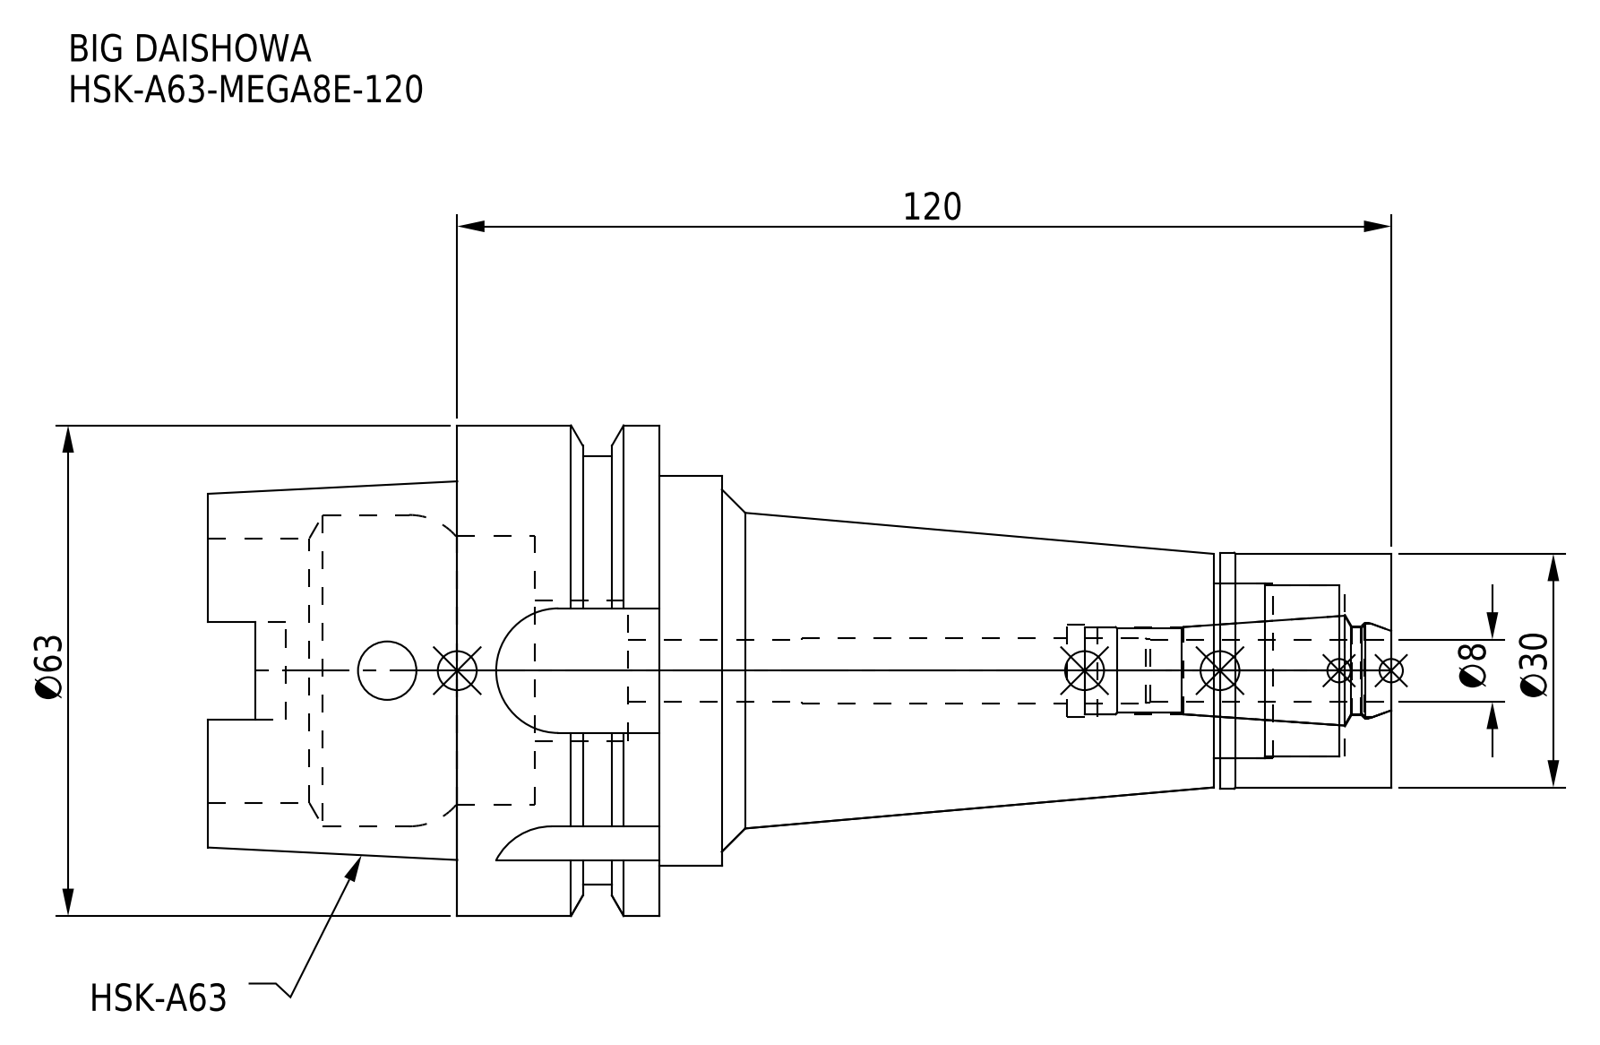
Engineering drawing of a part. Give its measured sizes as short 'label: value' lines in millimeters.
name: HA63ME08120-080_ASM.stp; HSK-A63-MEGA8E-120_1.stp; DXF_TEMP_ASSY_ASM_4_ASM.stp; HSK-A63-MEGA8E-120-080-FreeParts (+3 more)
written by: SolidWorks 2019 (CONFIG_CONTROL_DESIGN)
unit: mm
bodies: 2 solids, 127 faces (45 planar, 54 cylindrical, 28 other)
size: 152 × 63 × 63
volume: 169 239 mm³; area: 38 283 mm²
holes: 1× ⌀7.5, 1× ⌀8, 1× ⌀8.4, 1× ⌀11.2, 1× ⌀11.4, 1× ⌀11.8, 1× ⌀12.3, 1× ⌀18, 1× ⌀22, 1× ⌀22.5, 1× ⌀34, 1× ⌀34.5
bosses: 1× ⌀63, 1× ⌀55, 1× ⌀50, 1× ⌀30.3, 1× ⌀30
rounds: 2× R2.8, 2× R2.88, 2× R8, 1× R9
face distances: 26, 120, 16.05, 9.95, 94, 110.05, 152, 58, 41.95, 32
